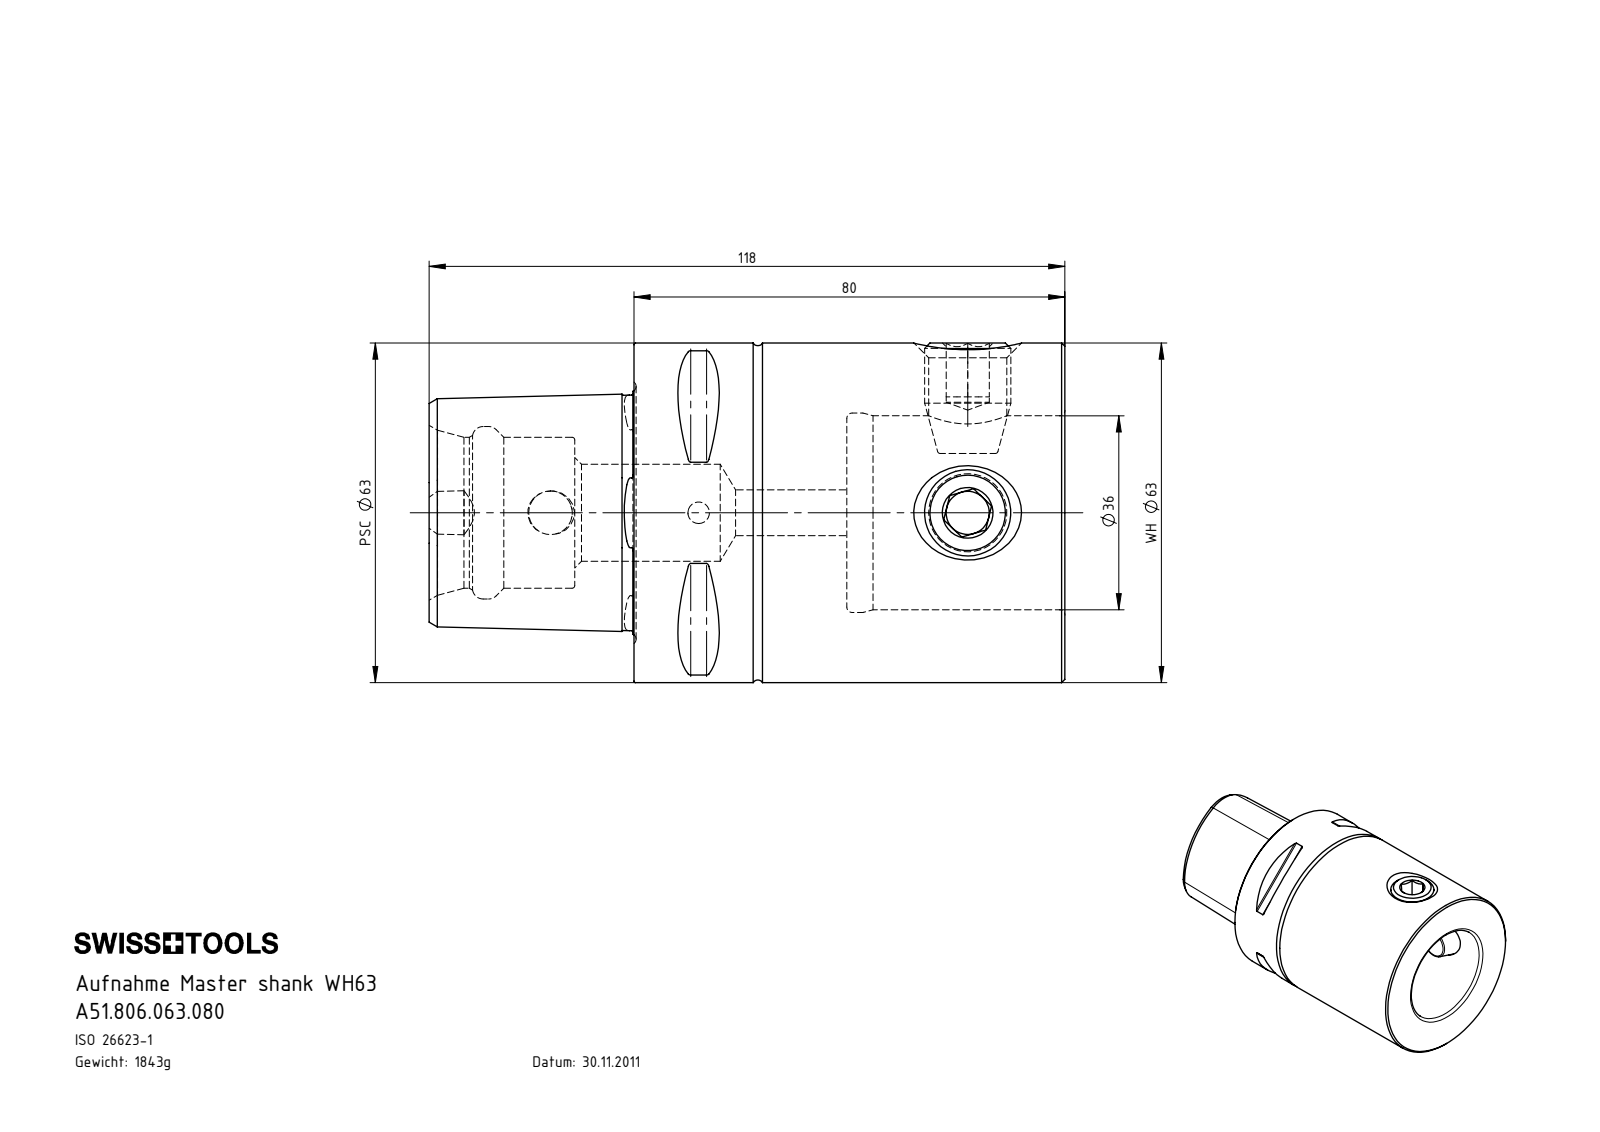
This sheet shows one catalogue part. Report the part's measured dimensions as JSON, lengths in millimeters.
{"part_name": "PS6-WH6.K01.080_B; A51.806.063.080; WH6-ER1.001.021", "step_written_by": "SolidWorks 2022 (AUTOMOTIVE_DESIGN)", "units": "millimeters", "bodies": {"solids": 3, "faces": 202, "planar": 48, "cylindrical": 45, "other": 109}, "overall_size": [118, 63, 63], "volume_mm3": 234782, "surface_area_mm2": 40013, "round_holes": [[8, 2], [14.5, 2], [4, 1], [8.1, 1], [8.5, 1], [18, 1], [28, 1], [32, 1], [36, 1], [37, 1]], "round_bosses_or_shafts": [[16, 2], [63, 1]], "partial_cylinders_radius": [[0.5, 8], [6, 1]], "face_to_face_distances": [80, 39.5, 40.5, 38, 77.5, 118, 24.88, 27, 11, 50.5], "hole_center_spacings": [27.5, 49.95, 77.45]}
